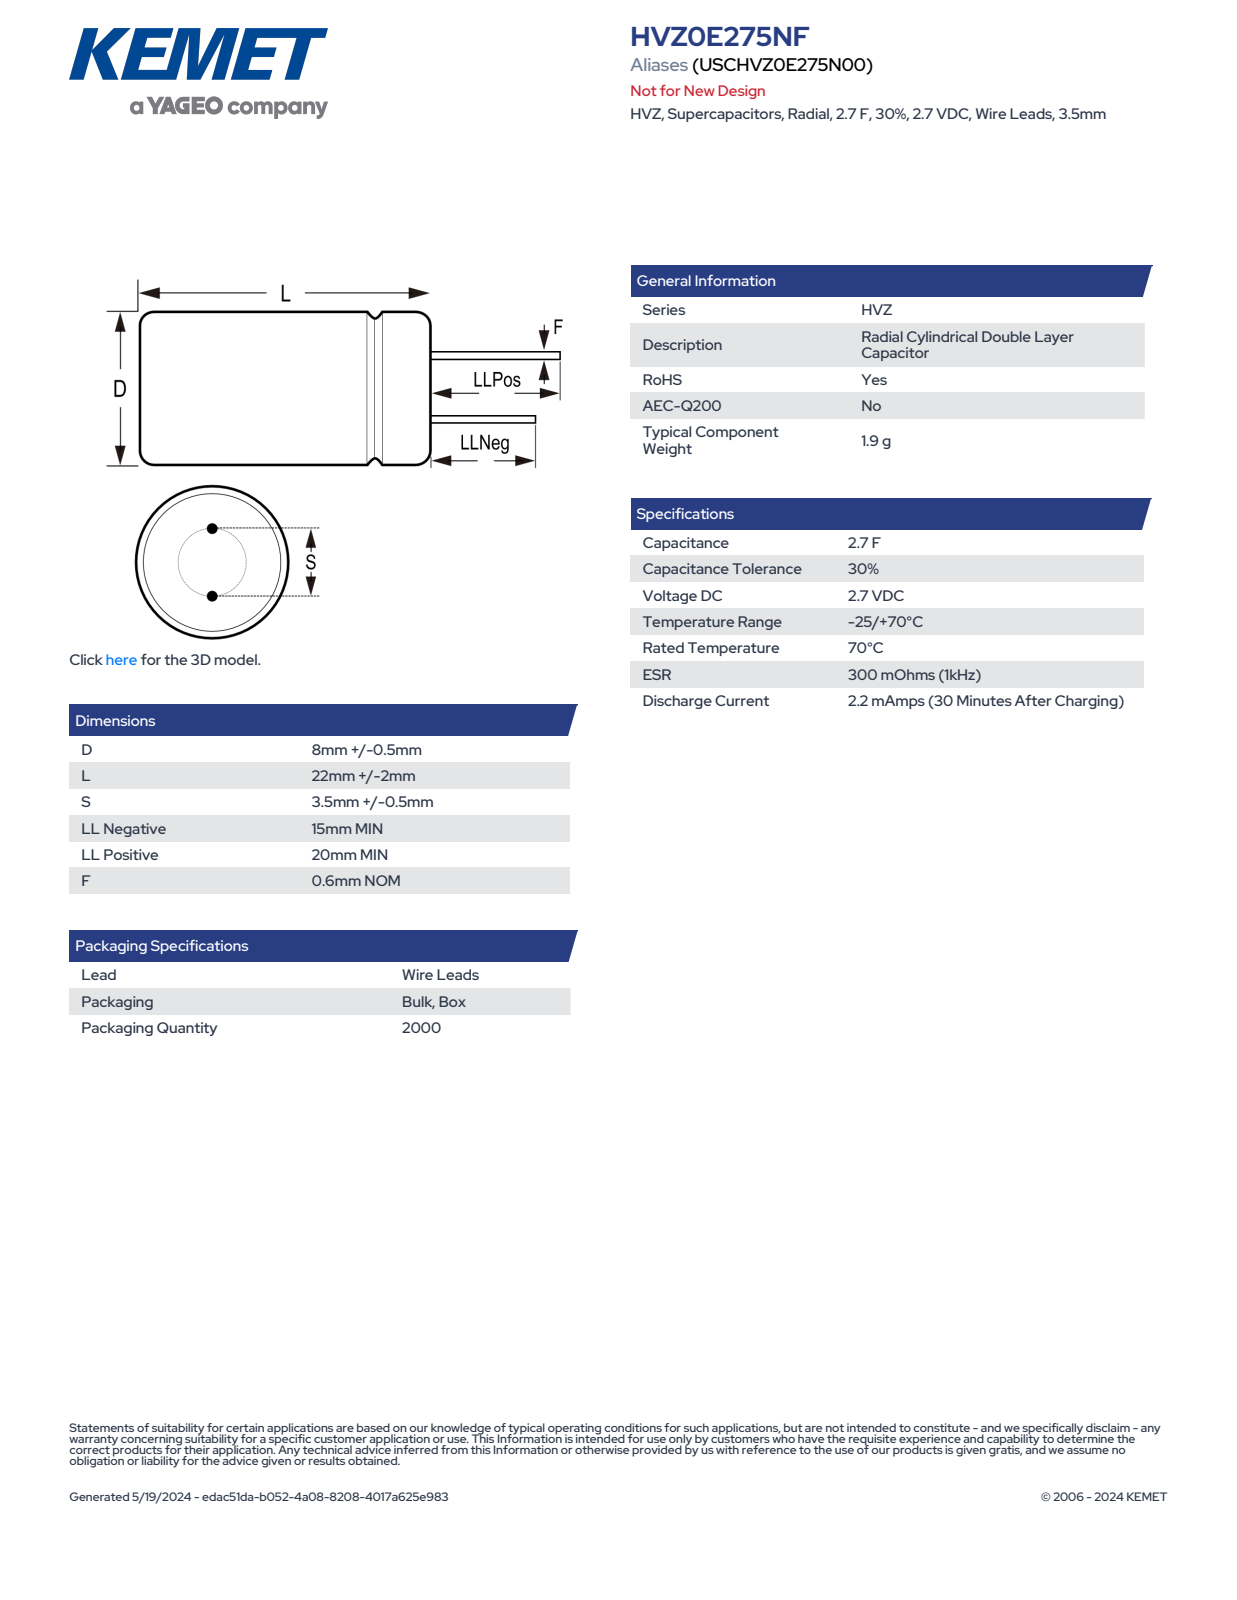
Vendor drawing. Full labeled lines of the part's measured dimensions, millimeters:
Part name (STEP PRODUCT): CDR_CCW_D8.5L24S3.5F0.6
STEP written by: SolidWorks 2014 (AUTOMOTIVE_DESIGN)
Units: millimetres
Bodies: 1 solid, 82 faces (26 planar, 17 cylindrical, 39 other)
Overall size (bounding box): 44 × 8.51 × 8.5
Volume: 1 364 mm³ · Surface area: 803 mm²
Round bosses / shafts (diameter × count): ⌀0.6 ×2, ⌀8.5 ×1
Partial cylindrical surfaces — rounded edges, fillets, slot ends (radius × count): R4.26 ×1
Main face-to-face distances: 24, 44, 20, 39, 15, 5
